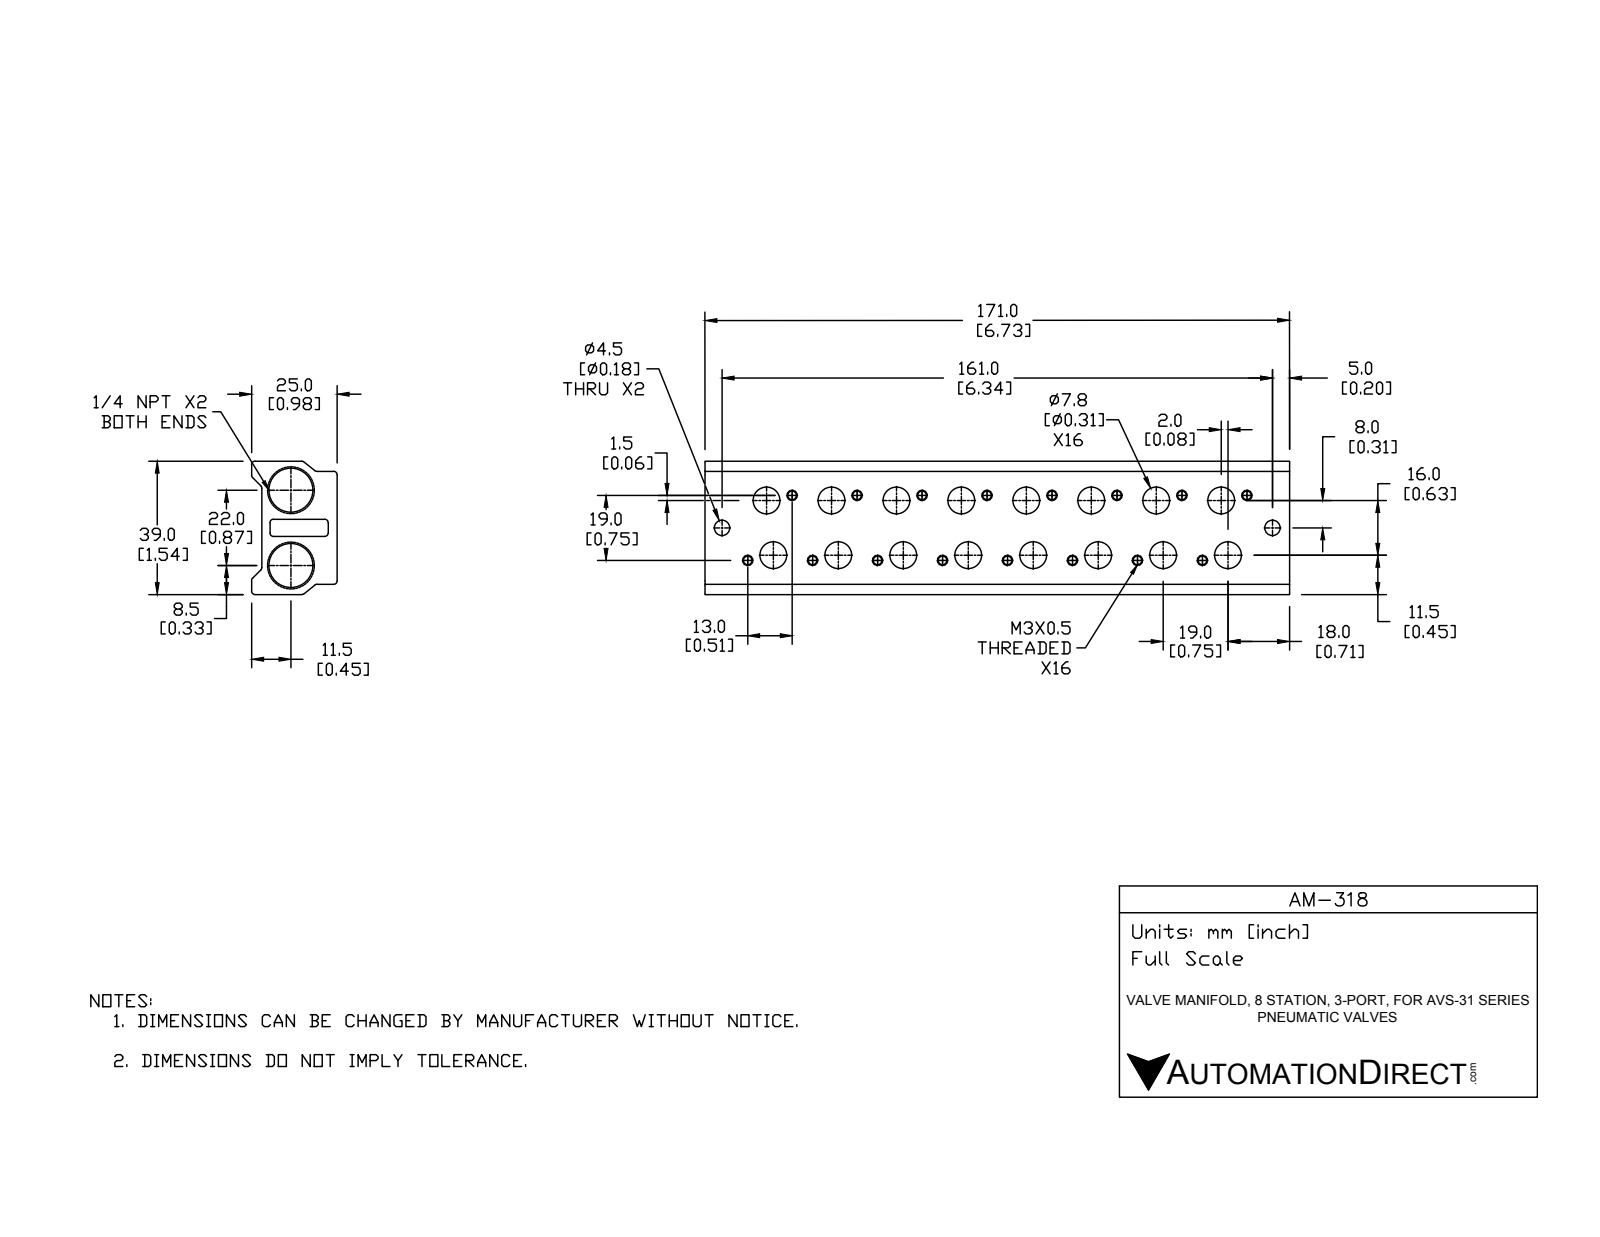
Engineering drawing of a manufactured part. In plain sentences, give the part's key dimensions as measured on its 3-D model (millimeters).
The part is named "AM-318". Its 3-D file was written by "SolidWorks 2018 (AUTOMOTIVE_DESIGN)". It is 1 solid with 210 faces: 26 planar, 110 cylindrical and 74 other. Overall it measures 171 by 39 by 25 millimeters. Its volume is 87 122 cubic millimeters and its surface area 44 946 square millimeters. Round holes: 16 of diameter 2.5, 16 of diameter 7.8, 2 of diameter 4.5, 2 of diameter 11.11, 2 of diameter 11.13. Partial cylindrical surfaces (rounded edges, fillets, slot ends): 16 of radius 1. The main face-to-face distances are 22, 17, 3, 5, 39, 36, 14, 19, 25, 33. The hole center spacings are 19, 38, 57, 7.65, 18.34, 76, 11.6, 22.1.
